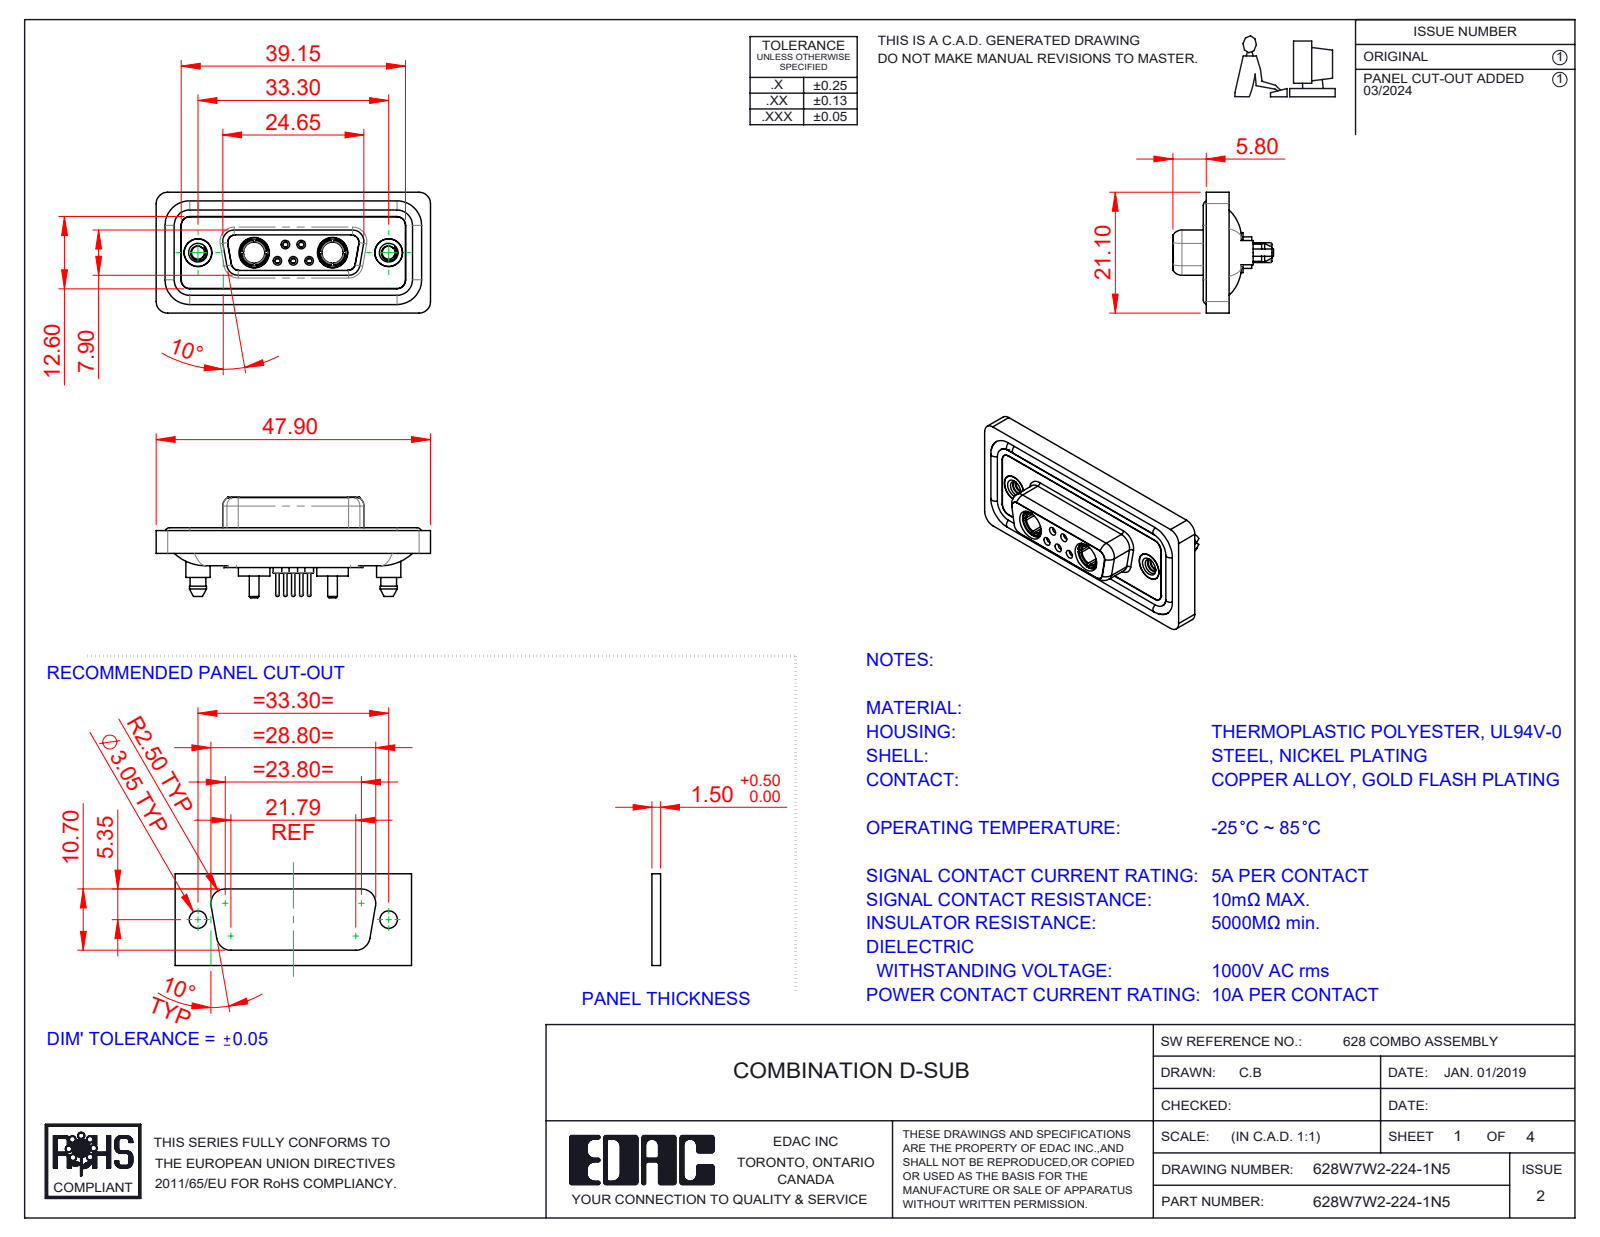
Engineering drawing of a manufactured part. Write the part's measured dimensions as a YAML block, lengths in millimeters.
part_name: "628W7W2-224-1N5; 628Combo Threaded Boardlock_5; 628Combo Waterproof Housing_15 Contacts; 628Combo Contact Row 1_24 (+5 more)"
step_written_by: "SolidWorks 2023 (CONFIG_CONTROL_DESIGN)"
units: millimeters
bodies: {solids: 16, faces: 859, planar: 254, cylindrical: 361, other: 244}
overall_size: [47.9, 21.1, 17.55]
volume: 6181
surface_area: 10193
round_holes:
  - {diameter: 0.9, count: 5}
  - {diameter: 1.1, count: 5}
  - {diameter: 1.5, count: 5}
  - {diameter: 2, count: 5}
  - {diameter: 4.85, count: 4}
  - {diameter: 1.6, count: 3}
  - {diameter: 1.7, count: 2}
  - {diameter: 2.26, count: 2}
  - {diameter: 3.7, count: 2}
  - {diameter: 4, count: 2}
  - {diameter: 4.05, count: 2}
  - {diameter: 5, count: 2}
round_bosses_or_shafts:
  - {diameter: 1.6, count: 6}
  - {diameter: 2.2, count: 5}
  - {diameter: 0.6, count: 5}
  - {diameter: 5.5, count: 2}
  - {diameter: 5.4, count: 2}
  - {diameter: 5.2, count: 2}
  - {diameter: 4.96, count: 2}
  - {diameter: 4.95, count: 2}
partial_cylinders:
  - {radius: 1.5, count: 24}
  - {radius: 2, count: 20}
  - {radius: 1.35, count: 12}
  - {radius: 1.6, count: 10}
  - {radius: 0.25, count: 4}
  - {radius: 0.5, count: 4}
  - {radius: 0.6, count: 4}
  - {radius: 0.65, count: 4}
face_to_face_distances: [0.4, 1.8, 1.6, 0.5, 2.9, 1.1, 7.45, 5.65, 6.6, 7.05]
hole_center_spacings: [3.16, 2.77, 9.8, 23.5, 4.31, 4.33, 5.03, 5.04]
